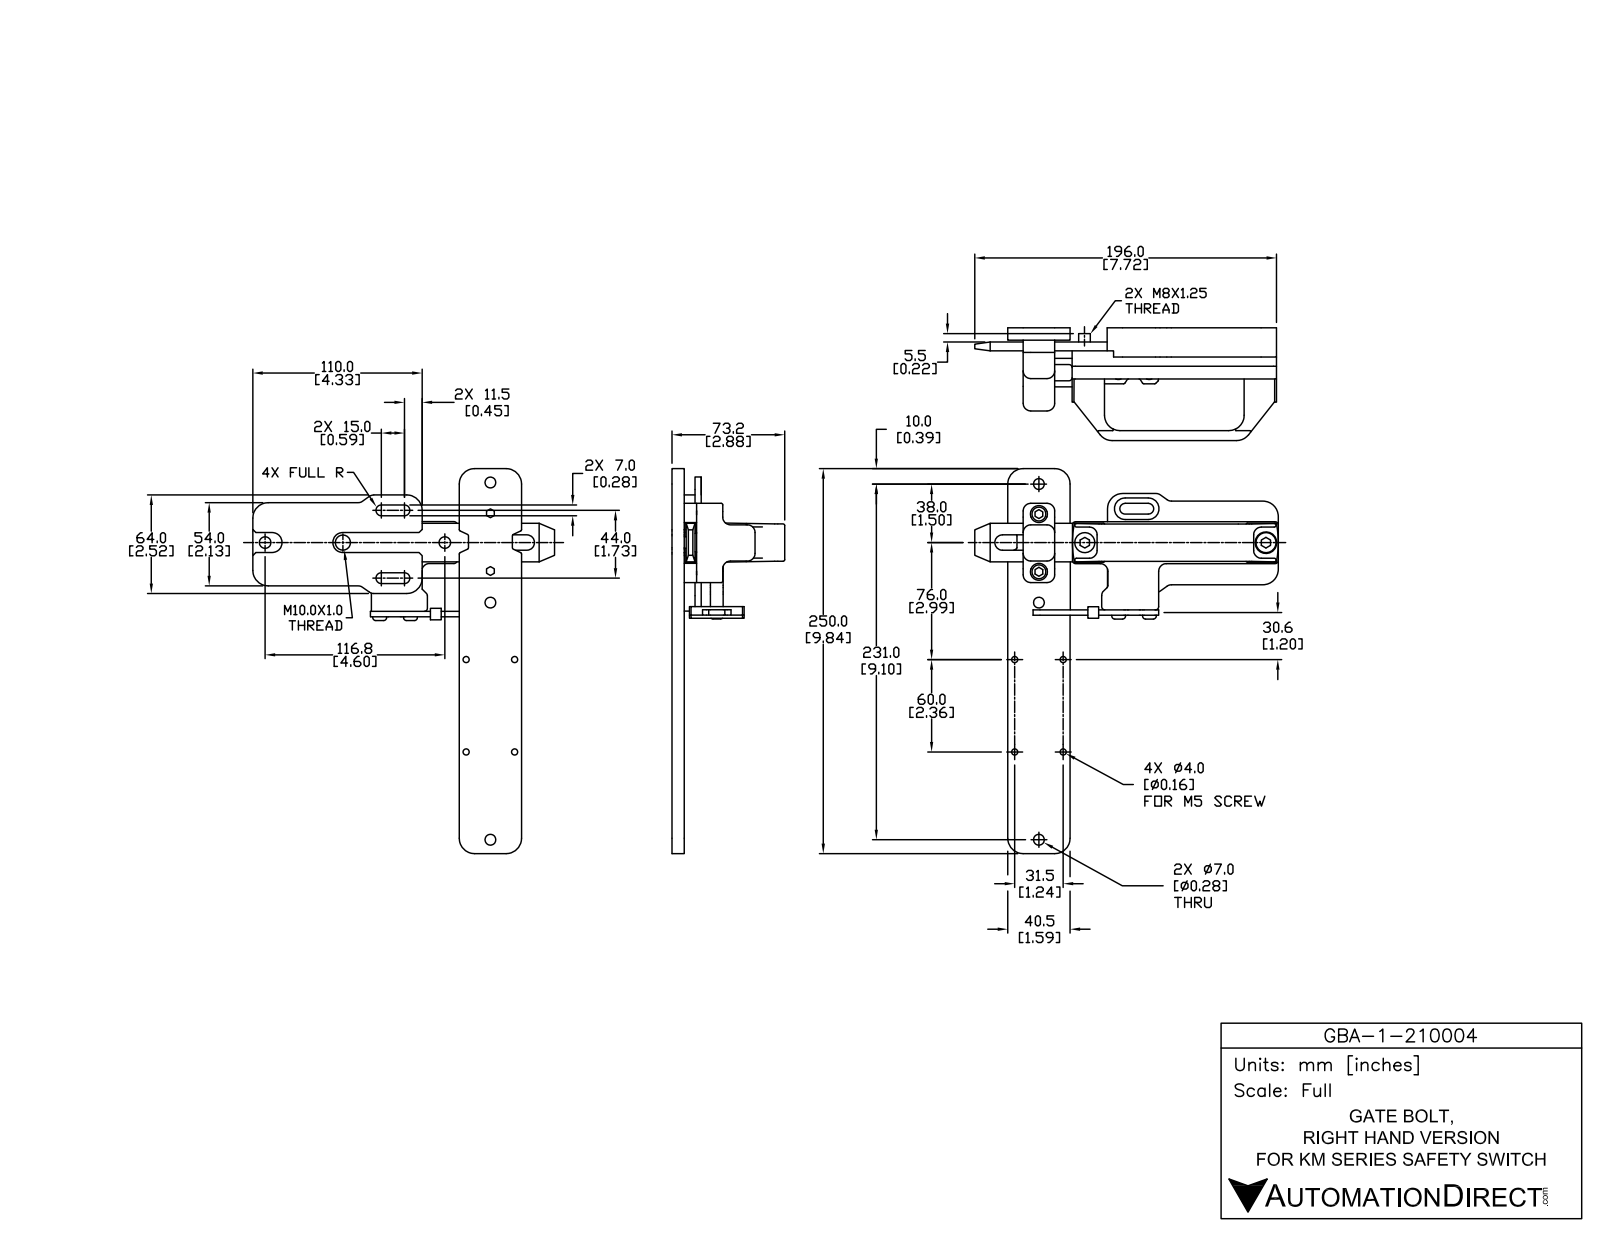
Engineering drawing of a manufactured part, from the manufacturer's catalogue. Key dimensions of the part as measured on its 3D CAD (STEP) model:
Part name (STEP PRODUCT): GBA-1-210004
STEP written by: SolidWorks 2019 (AUTOMOTIVE_DESIGN)
Units: millimetres
Bodies: 15 solids, 861 faces (308 planar, 351 cylindrical, 202 other)
Overall size (bounding box): 250 × 248.1 × 78.8
Volume: 306 389 mm³ · Surface area: 114 462 mm²
Round holes (diameter × count): ⌀4 ×4, ⌀4.2 ×2, ⌀5 ×2, ⌀5.5 ×2, ⌀6.5 ×2, ⌀6.75 ×2, ⌀6.8 ×2, ⌀8.3 ×2, ⌀8.6 ×2, ⌀8.8 ×2, ⌀11 ×2, ⌀14 ×2
Round bosses / shafts (diameter × count): ⌀13 ×2, ⌀10 ×2, ⌀9.3 ×2, ⌀8 ×2, ⌀6 ×2, ⌀5 ×2
Partial cylindrical surfaces — rounded edges, fillets, slot ends (radius × count): R0.5 ×110, R0.1 ×56, R1 ×38, R3 ×16, R5 ×16, R2 ×14, R8 ×8, R3.45 ×6
Main face-to-face distances: 8, 23.8, 10, 19, 6, 7.8, 16, 15.8, 13.8, 5.8
Hole centre spacings: 20, 30, 57.97, 59.91, 60, 67.08, 95.19, 103.67
